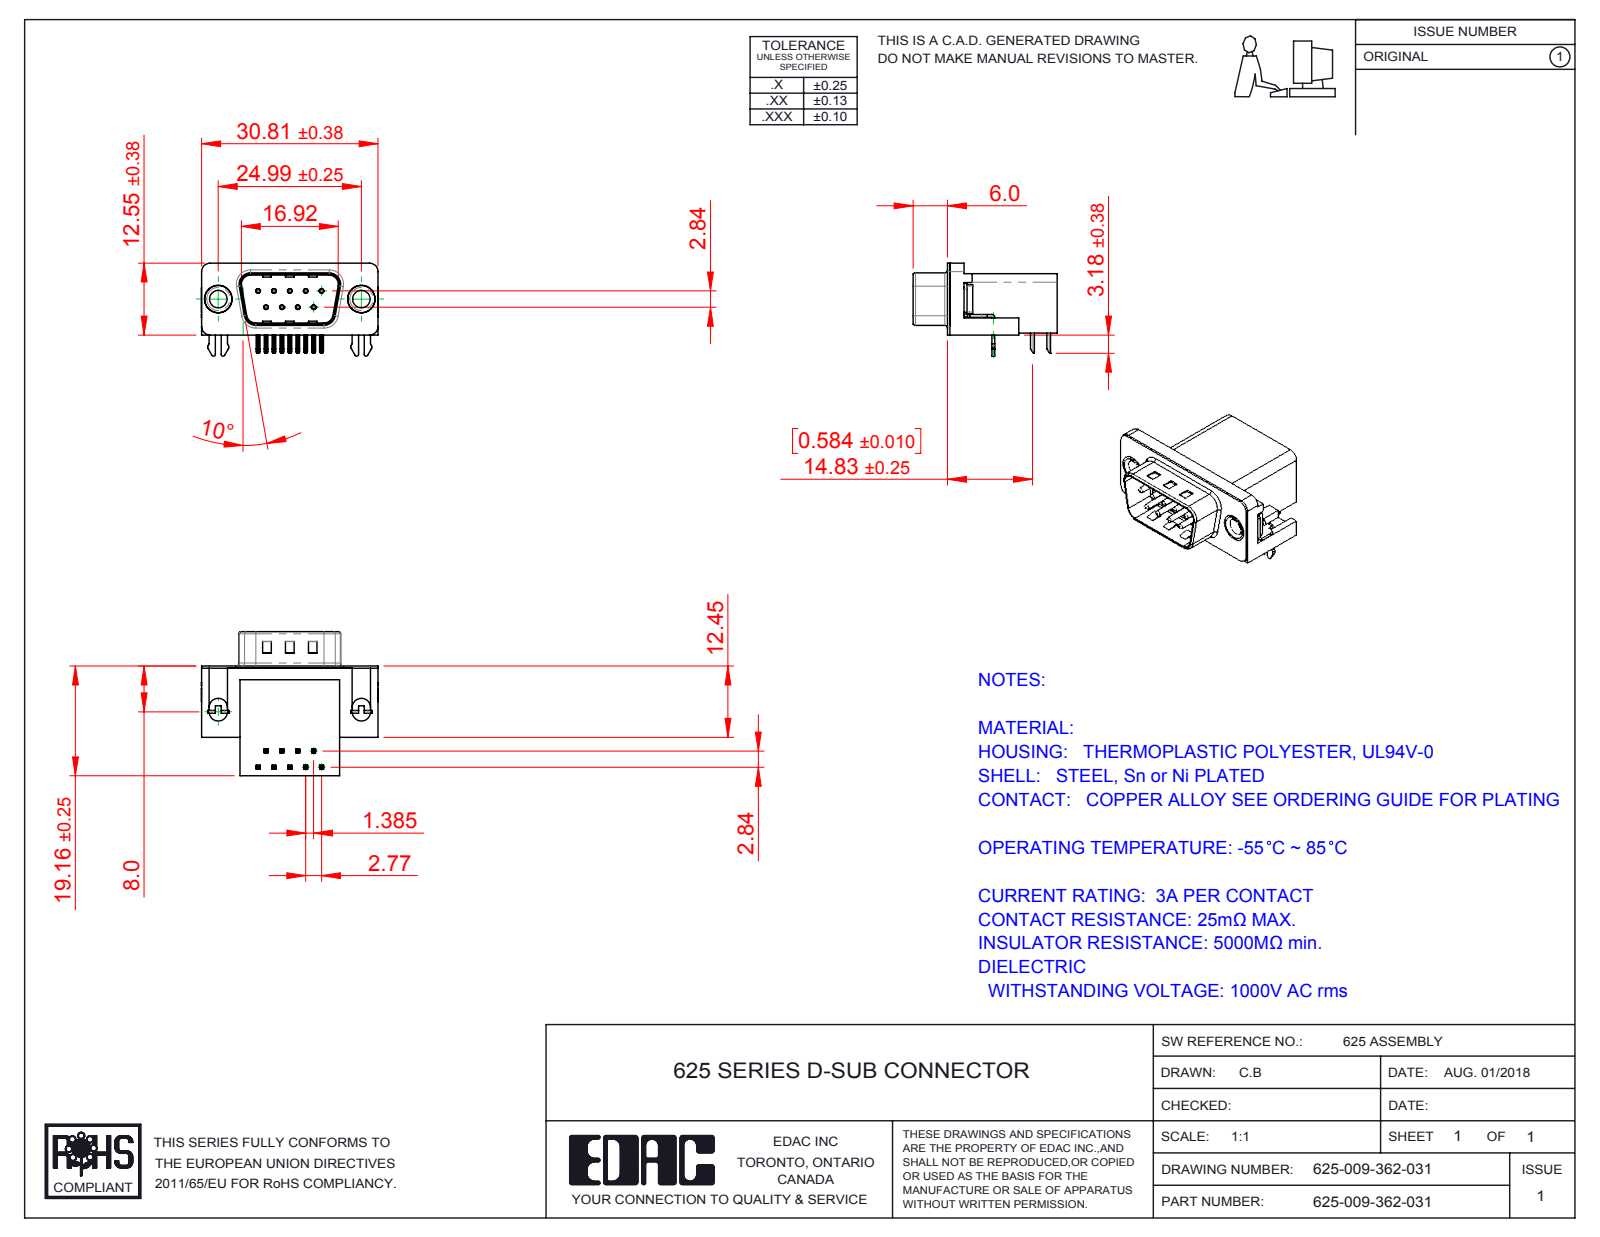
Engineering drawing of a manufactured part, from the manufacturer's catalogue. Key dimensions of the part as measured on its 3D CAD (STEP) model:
Part name (STEP PRODUCT): 625 Thru Hole Rivet; 625 2 Prong Board Lock; 625 Contact Bottom; 625 Contact Top (+3 more)
STEP written by: SolidWorks 2016 (CONFIG_CONTROL_DESIGN)
Units: millimetres
Bodies: 15 solids, 993 faces (605 planar, 307 cylindrical, 81 other)
Overall size (bounding box): 30.89 × 25.16 × 16.25
Volume: 4 462 mm³ · Surface area: 4 934 mm²
Round holes (diameter × count): ⌀0.35 ×9, ⌀0.8 ×9, ⌀3.05 ×2, ⌀4 ×2, ⌀4.8 ×2, ⌀5 ×2
Round bosses / shafts (diameter × count): ⌀0.75 ×9, ⌀4.9 ×2, ⌀4.75 ×2, ⌀3.85 ×2
Partial cylindrical surfaces — rounded edges, fillets, slot ends (radius × count): R0.25 ×44, R0.12 ×18, R1 ×16, R0.5 ×14, R1.5 ×8, R1.6 ×8, R0.32 ×4, R0.9 ×4
Main face-to-face distances: 0.4, 10.34, 18.76, 19.16, 16.26, 2.5, 2.9, 0.35, 10.69, 0.5
Hole centre spacings: 3.16, 2.77, 5.54, 5.03, 5.04, 8.31, 7.48, 7.49
